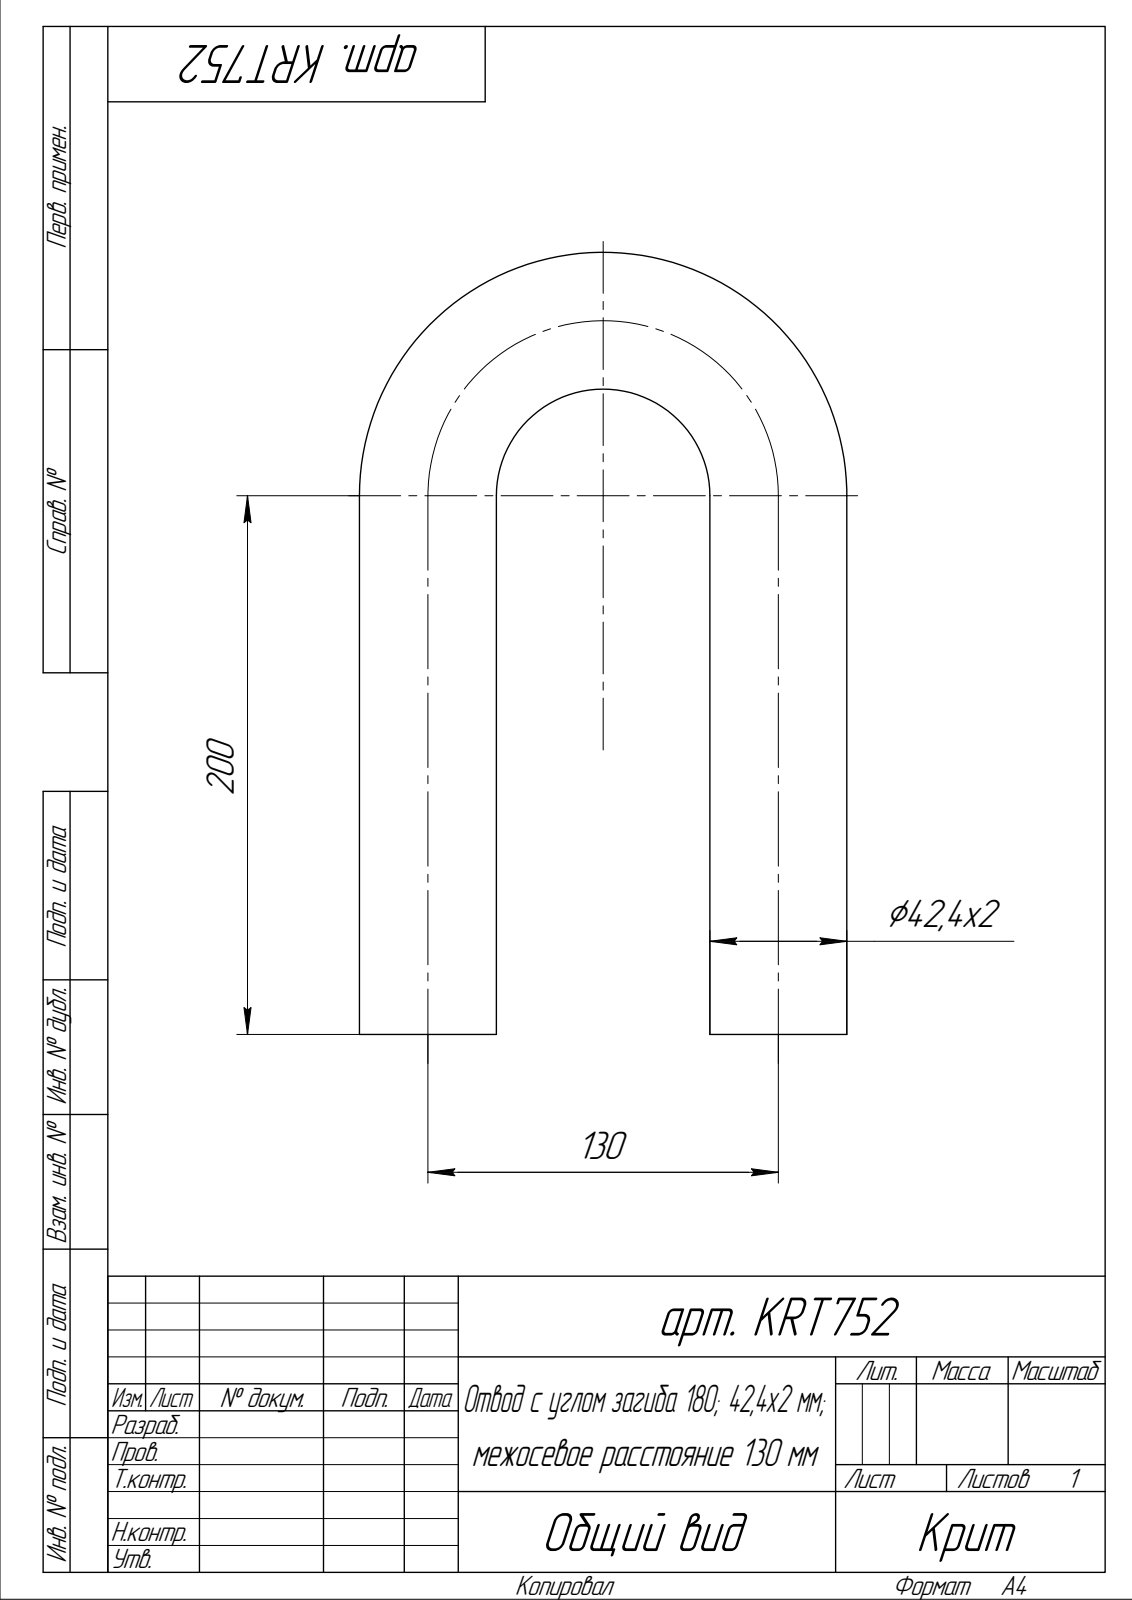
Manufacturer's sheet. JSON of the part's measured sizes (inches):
{"part_name": "арт. KRT752 Отвод с углом загиба 180; 42,4 толщина стенки 1,5 мм; межосевое расстояние 130 мм", "step_written_by": "ASCON Math Kernel (AUTOMOTIVE_DESIGN)", "units": "inches", "bodies": {"solids": 1, "faces": 8, "planar": 2, "cylindrical": 4, "other": 2}, "overall_size": [11.433, 7.118, 2], "volume_in3": 8.566, "surface_area_in2": 290.8, "round_holes": [[1.882, 2]], "round_bosses_or_shafts": [[2, 2]], "hole_center_spacings": [5.118]}
